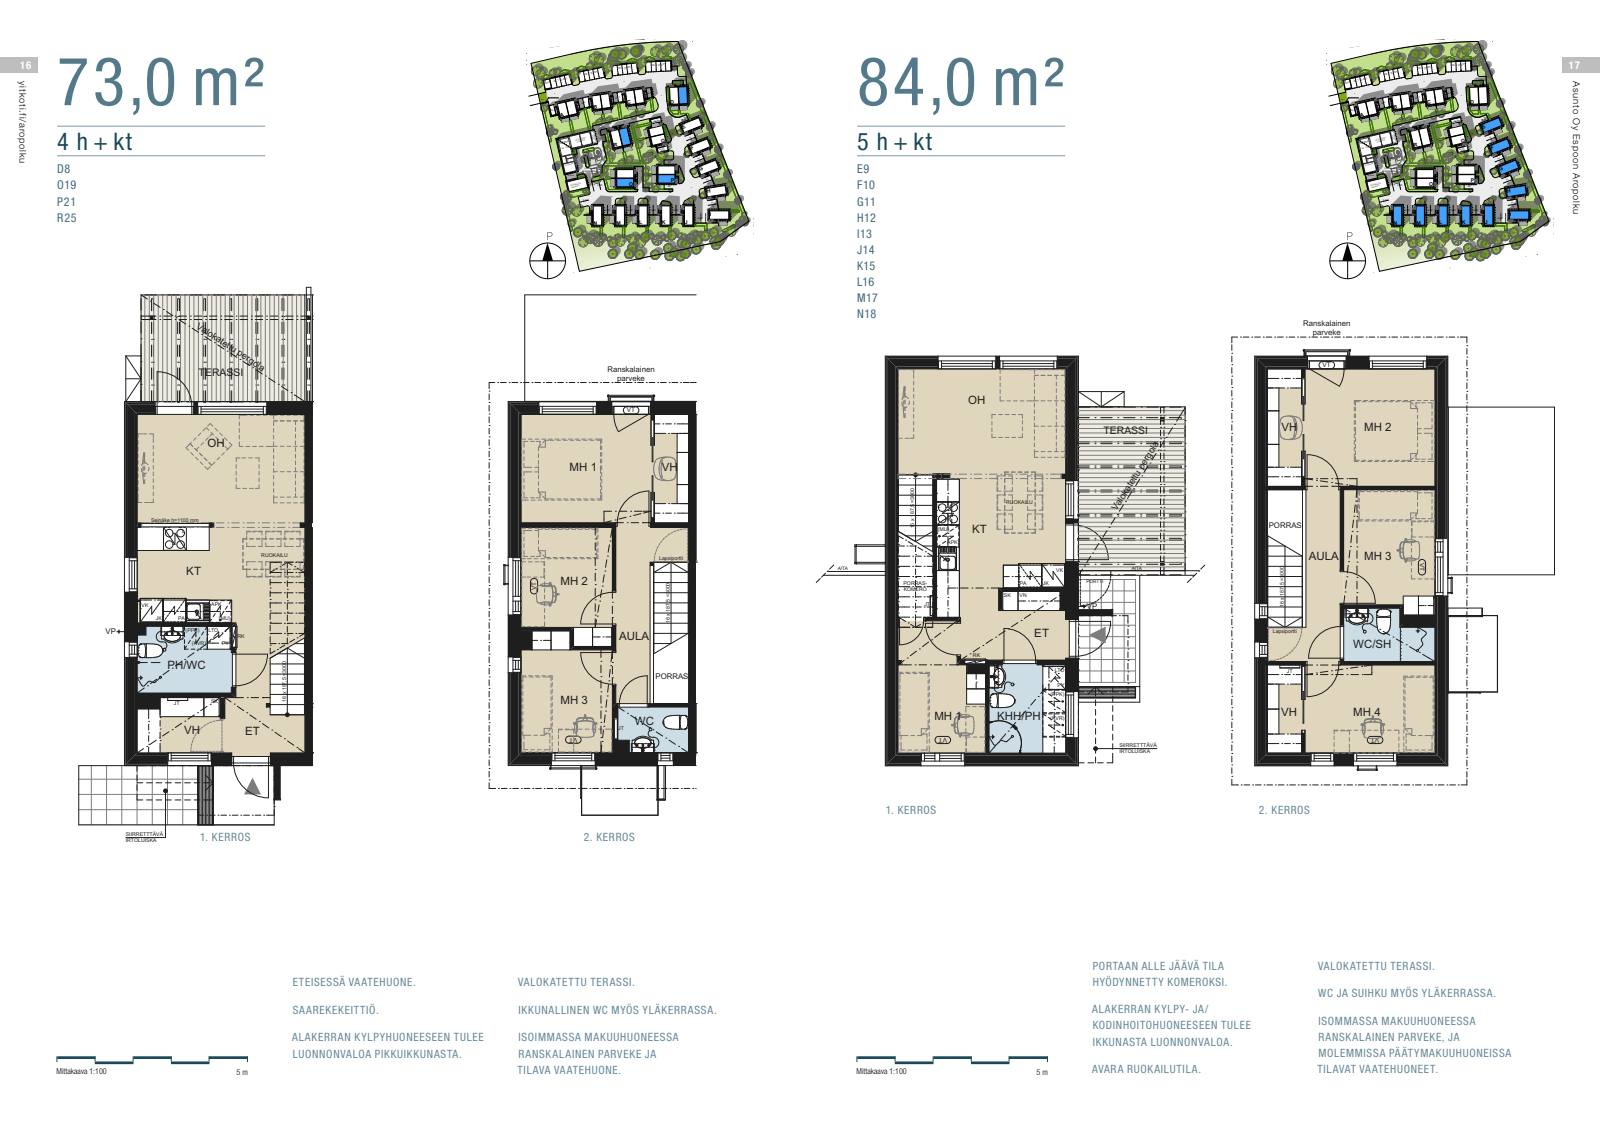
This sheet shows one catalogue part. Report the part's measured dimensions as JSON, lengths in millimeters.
{"step_written_by": "ACIS (automotive_design)", "units": "millimeters", "bodies": {"solids": 2, "faces": 30, "planar": 8, "cylindrical": 12, "other": 10}, "overall_size": [113, 8, 8], "volume_mm3": 4610, "surface_area_mm2": 2684, "round_bosses_or_shafts": [[8, 1], [6.8, 1]], "partial_cylinders_radius": [[0.64, 1], [1.05, 1], [1.45, 1], [3.9, 1]], "face_to_face_distances": [57.6, 0.41, 27.62, 29.98]}
